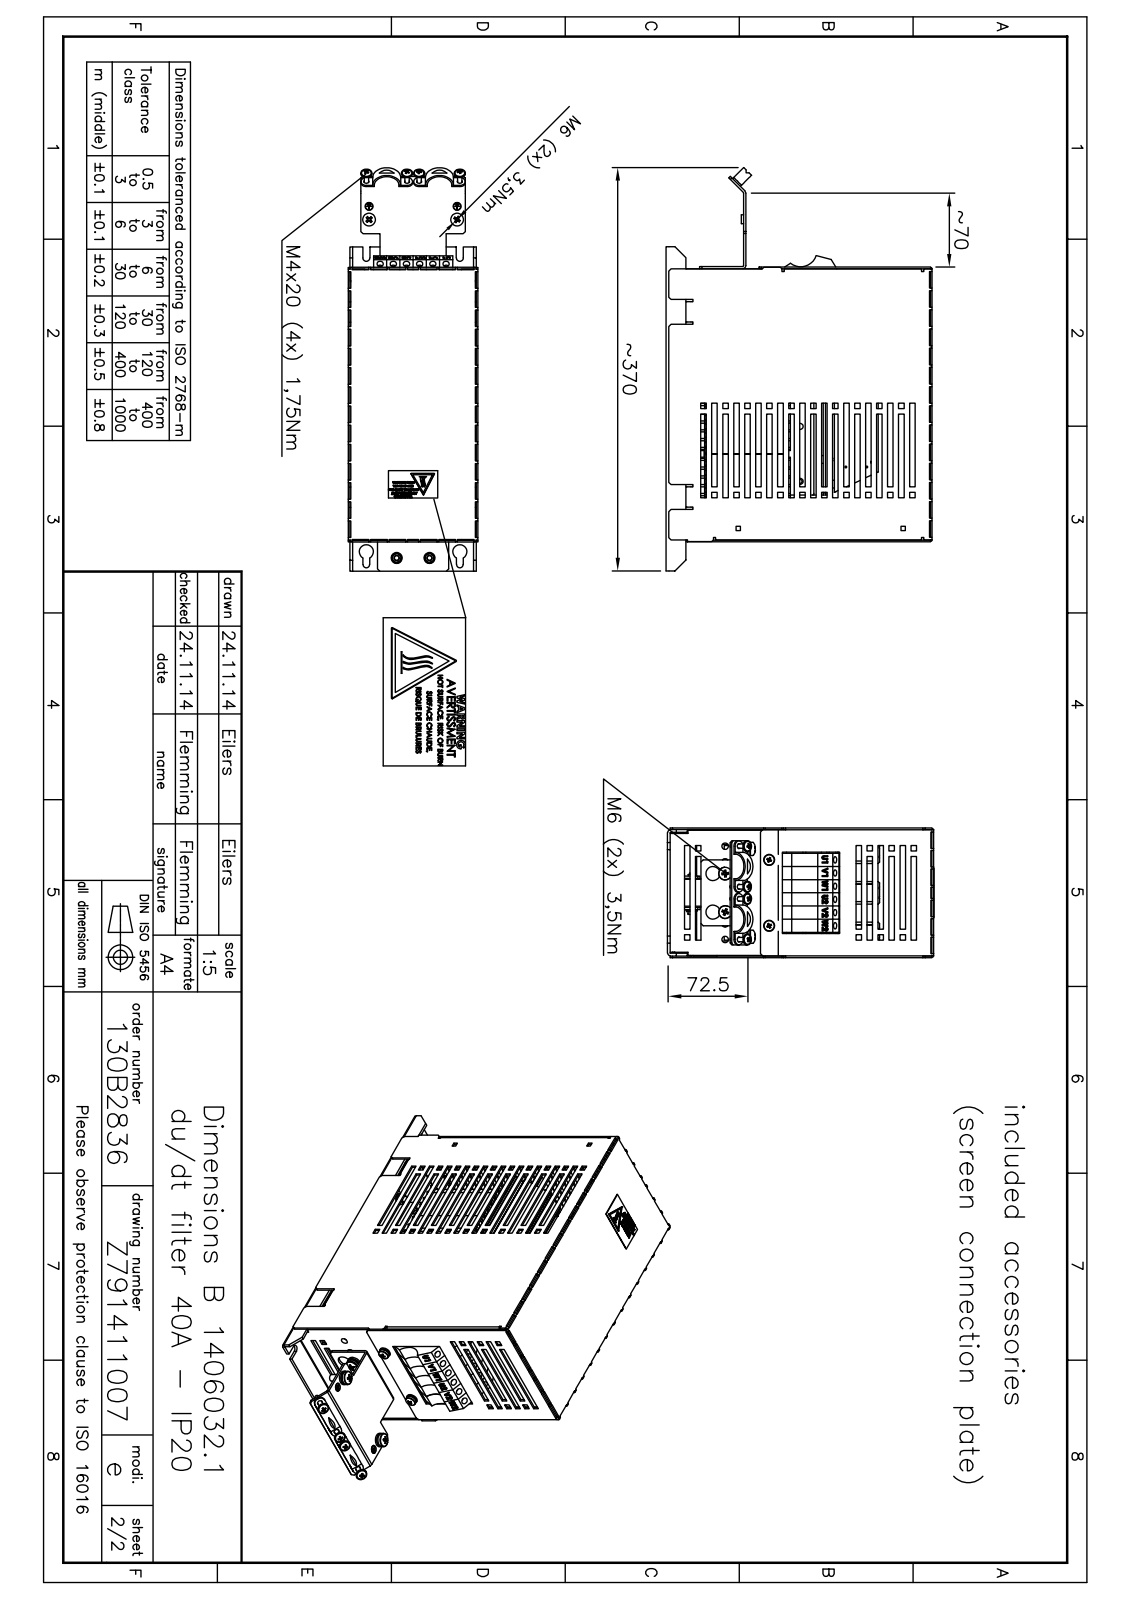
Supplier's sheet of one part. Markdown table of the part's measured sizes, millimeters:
| quantity | value |
| --- | --- |
| part name | TS35x72; hex nut style 1 gradeab_din_Hexagon Nut ISO 4032 - M5 - D - N; Warnschild.SLDPRT.; pan head cross recess screw_din_ISO 7045 - M5 x 10 - Z --- 10N (+8 more) |
| STEP written by | SolidWorks 2014 (AUTOMOTIVE_DESIGN) |
| units | millimeters |
| bodies | 139 solids, 7152 faces (4868 planar, 1292 cylindrical, 992 other) |
| overall size | 367.13 × 242.5 × 118 |
| volume | 1 426 000 mm³ |
| surface area | 992 916 mm² |
| round holes (diameter × count) | 5.5 × 16, 5 × 14, 1.71 × 12, 5.3 × 12, 5.7 × 12, 4.3 × 10, 2 × 8, 3 × 6, 3.3 × 6, 3.7 × 6, 4.2 × 6, 5.1 × 6 |
| round bosses / shafts (diameter × count) | 10 × 20, 8 × 12, 9 × 10, 4 × 10, 7 × 8, 6.5 × 8, 9.5 × 6, 9.2 × 6 |
| partial cylindrical surfaces (radius × count) | 0.2 × 160, 2 × 66, 0.4 × 36, 0.5 × 36, 0.65 × 36, 0.1 × 32, 0.3 × 18, 1.6 × 15 |
| main face-to-face distances | 1.5, 116.5, 2, 115, 118, 1, 46.75, 71.25, 45.25, 69.75 |
| hole center spacings | 1.92, 24, 12, 26.83, 37, 3.84, 8.32, 33.94 |
